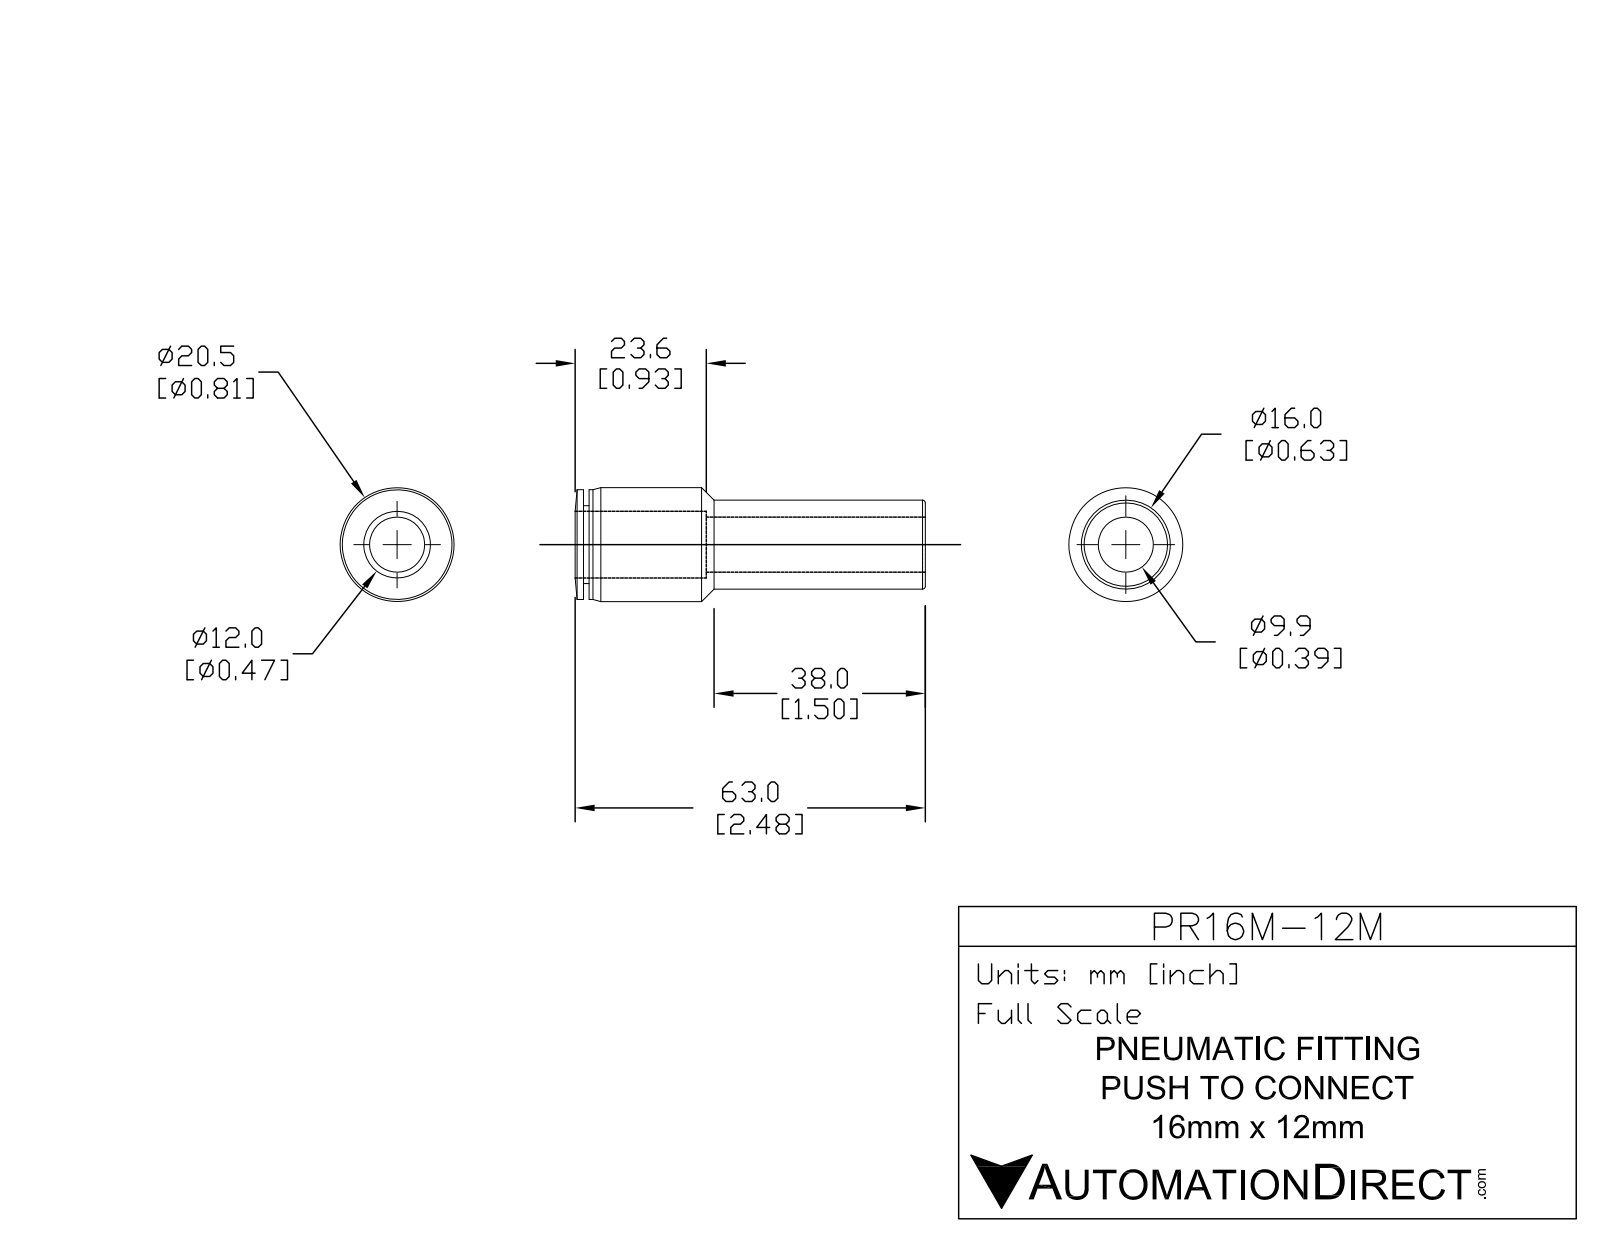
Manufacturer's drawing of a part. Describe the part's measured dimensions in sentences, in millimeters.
The part is named "PR16M-12M". Its 3-D file was written by "SolidWorks 2015 (CONFIG_CONTROL_DESIGN)". It is 1 solid with 26 faces: 4 planar, 14 cylindrical and 8 other. Overall it measures 63 by 20.5 by 20.5 millimeters. Its volume is 9 755 cubic millimeters and its surface area 6 275 square millimeters. Round holes: 1 of diameter 9.9, 1 of diameter 12. Round bosses or shafts: 1 of diameter 20.5, 1 of diameter 19.74, 1 of diameter 16, 1 of diameter 14. The main face-to-face distances are 1, 60.5, 61.5, 39.4, 21.1, 22.1.
